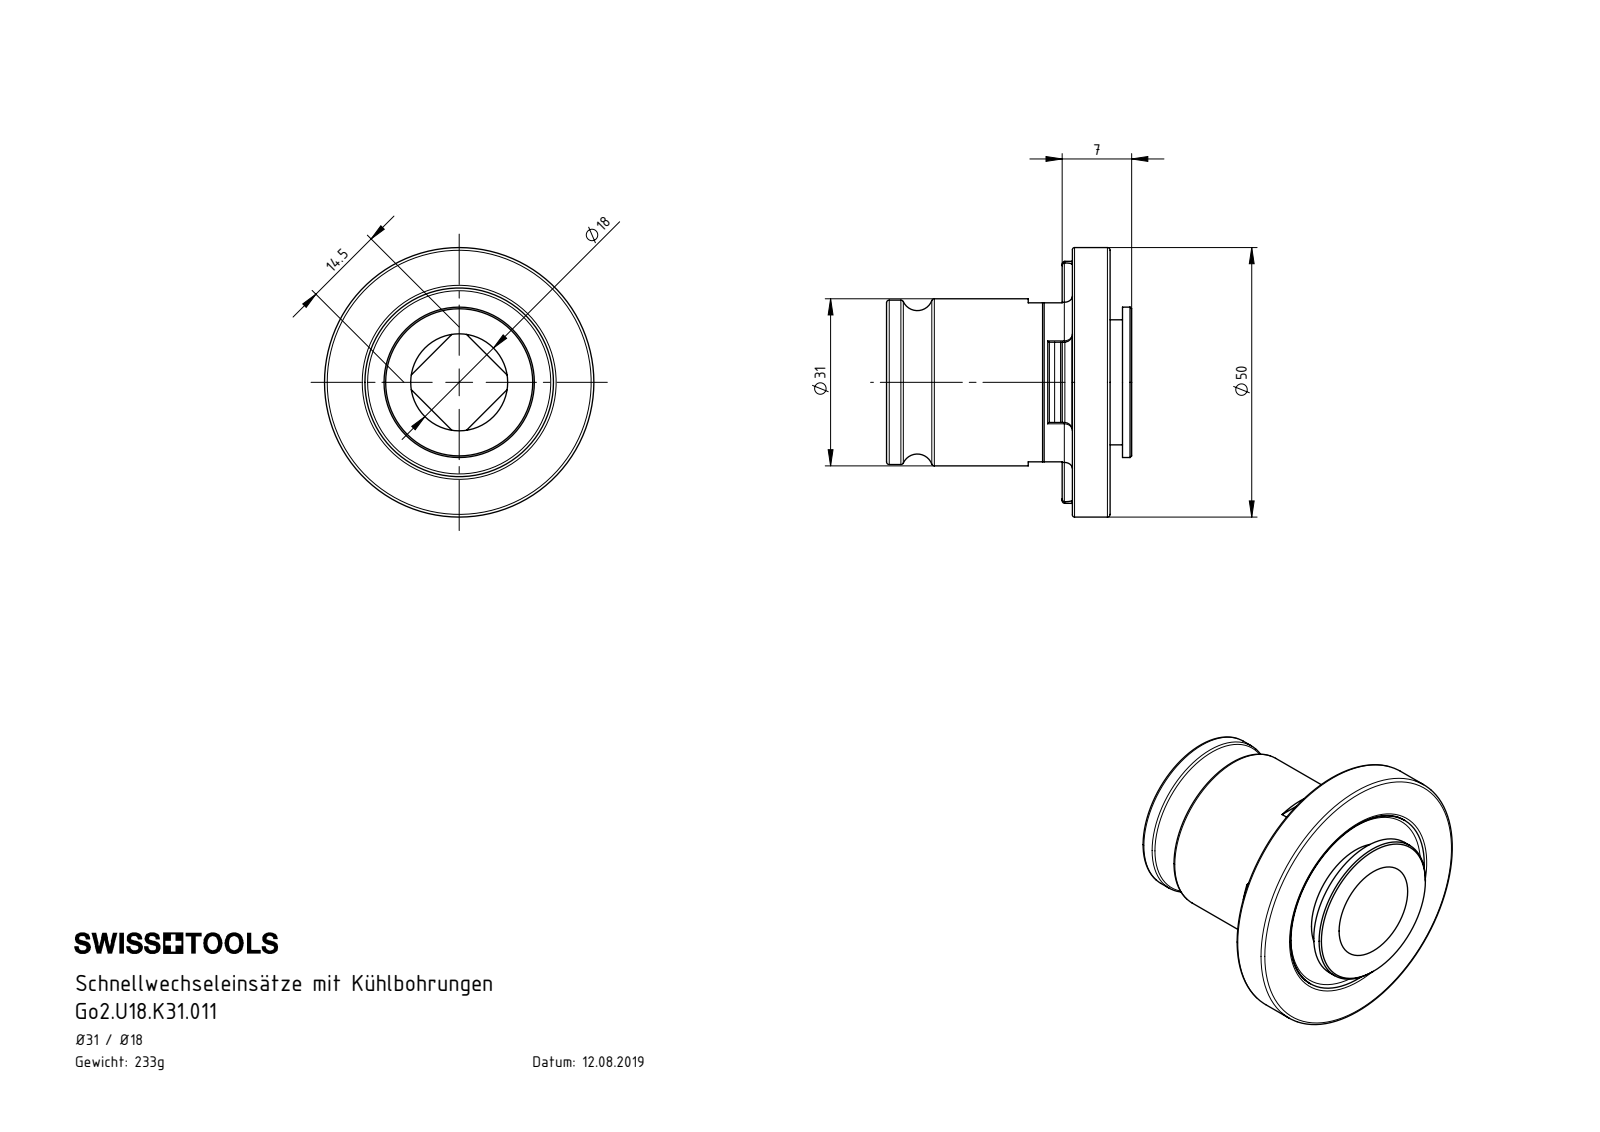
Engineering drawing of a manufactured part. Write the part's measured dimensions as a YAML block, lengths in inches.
part_name: "Go2.U18.K31.011_A"
step_written_by: "SolidWorks 2012 (AUTOMOTIVE_DESIGN)"
units: inches
bodies: {solids: 1, faces: 140, planar: 40, cylindrical: 41, other: 59}
overall_size: [1.969, 1.969, 1.791]
volume: 1.827
surface_area: 17.68
round_holes:
  - {diameter: 0.709, count: 1}
  - {diameter: 0.791, count: 1}
round_bosses_or_shafts:
  - {diameter: 1.969, count: 1}
  - {diameter: 1.378, count: 1}
  - {diameter: 1.22, count: 1}
  - {diameter: 1.205, count: 1}
  - {diameter: 1.201, count: 1}
  - {diameter: 1.102, count: 1}
  - {diameter: 0.953, count: 1}
partial_cylinders:
  - {radius: 0.059, count: 5}
  - {radius: 0.02, count: 4}
  - {radius: 0.787, count: 1}
  - {radius: 0.884, count: 1}
face_to_face_distances: [0.276, 0.25, 0.026, 0.433, 0.183, 0.157, 1.358, 1.608, 1.634, 1.791]
